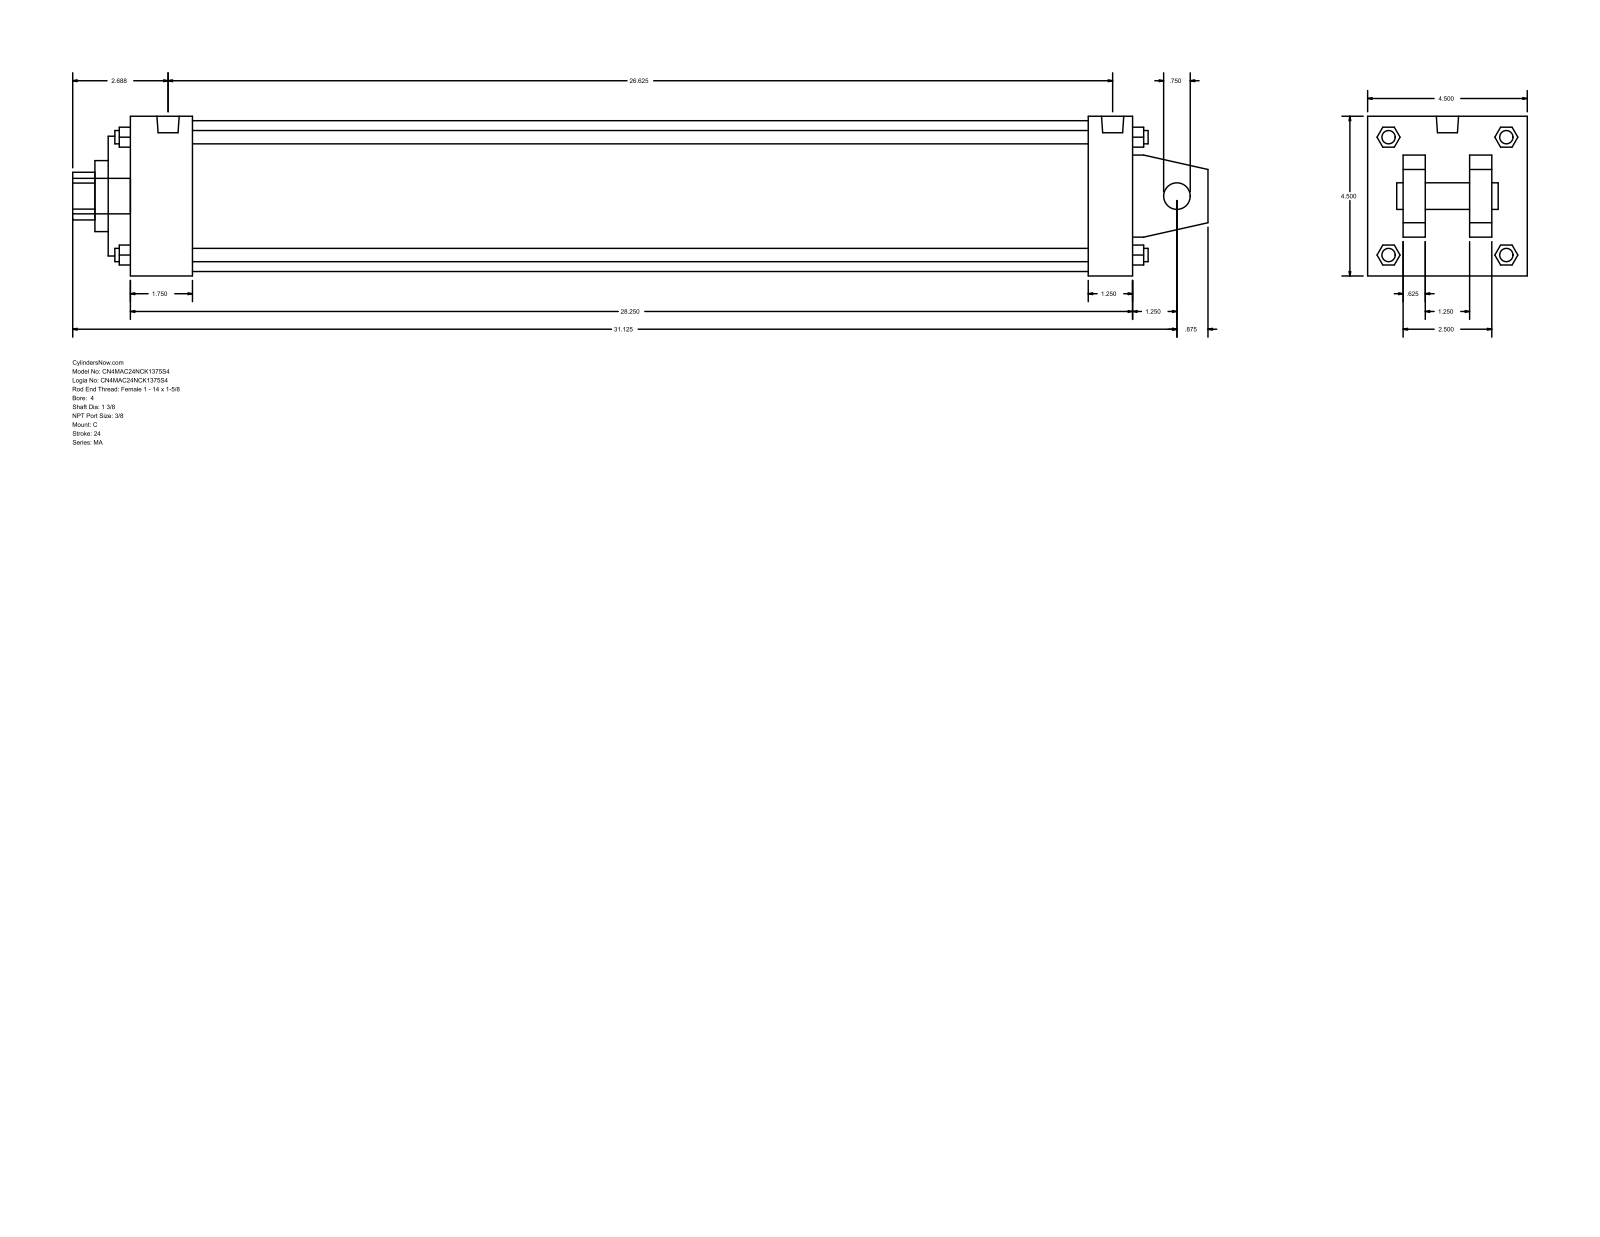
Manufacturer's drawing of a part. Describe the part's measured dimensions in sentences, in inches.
The part is named "MA_C__0400_1.375". Its 3-D file was written by "GSSL Pune (CONFIG_CONTROL_DESIGN)". It is 0 solids with 141 faces: 109 planar, 32 cylindrical and 0 other. Overall it measures 32 by 4.5 by 4.5 inches. Round holes: 1 of diameter 0.75, 1 of diameter 1.375, 1 of diameter 2, 1 of diameter 3.375, 1 of diameter 4.25. Round bosses or shafts: 4 of diameter 0.437, 4 of diameter 0.375, 2 of diameter 0.627, 1 of diameter 1. Partial cylindrical surfaces (rounded edges, fillets, slot ends): 1 of radius 0.672. The main face-to-face distances are 4.5, 0.625, 28.25, 2.875, 1.625, 1, 3.5, 1.875, 28.875, 27.625.
